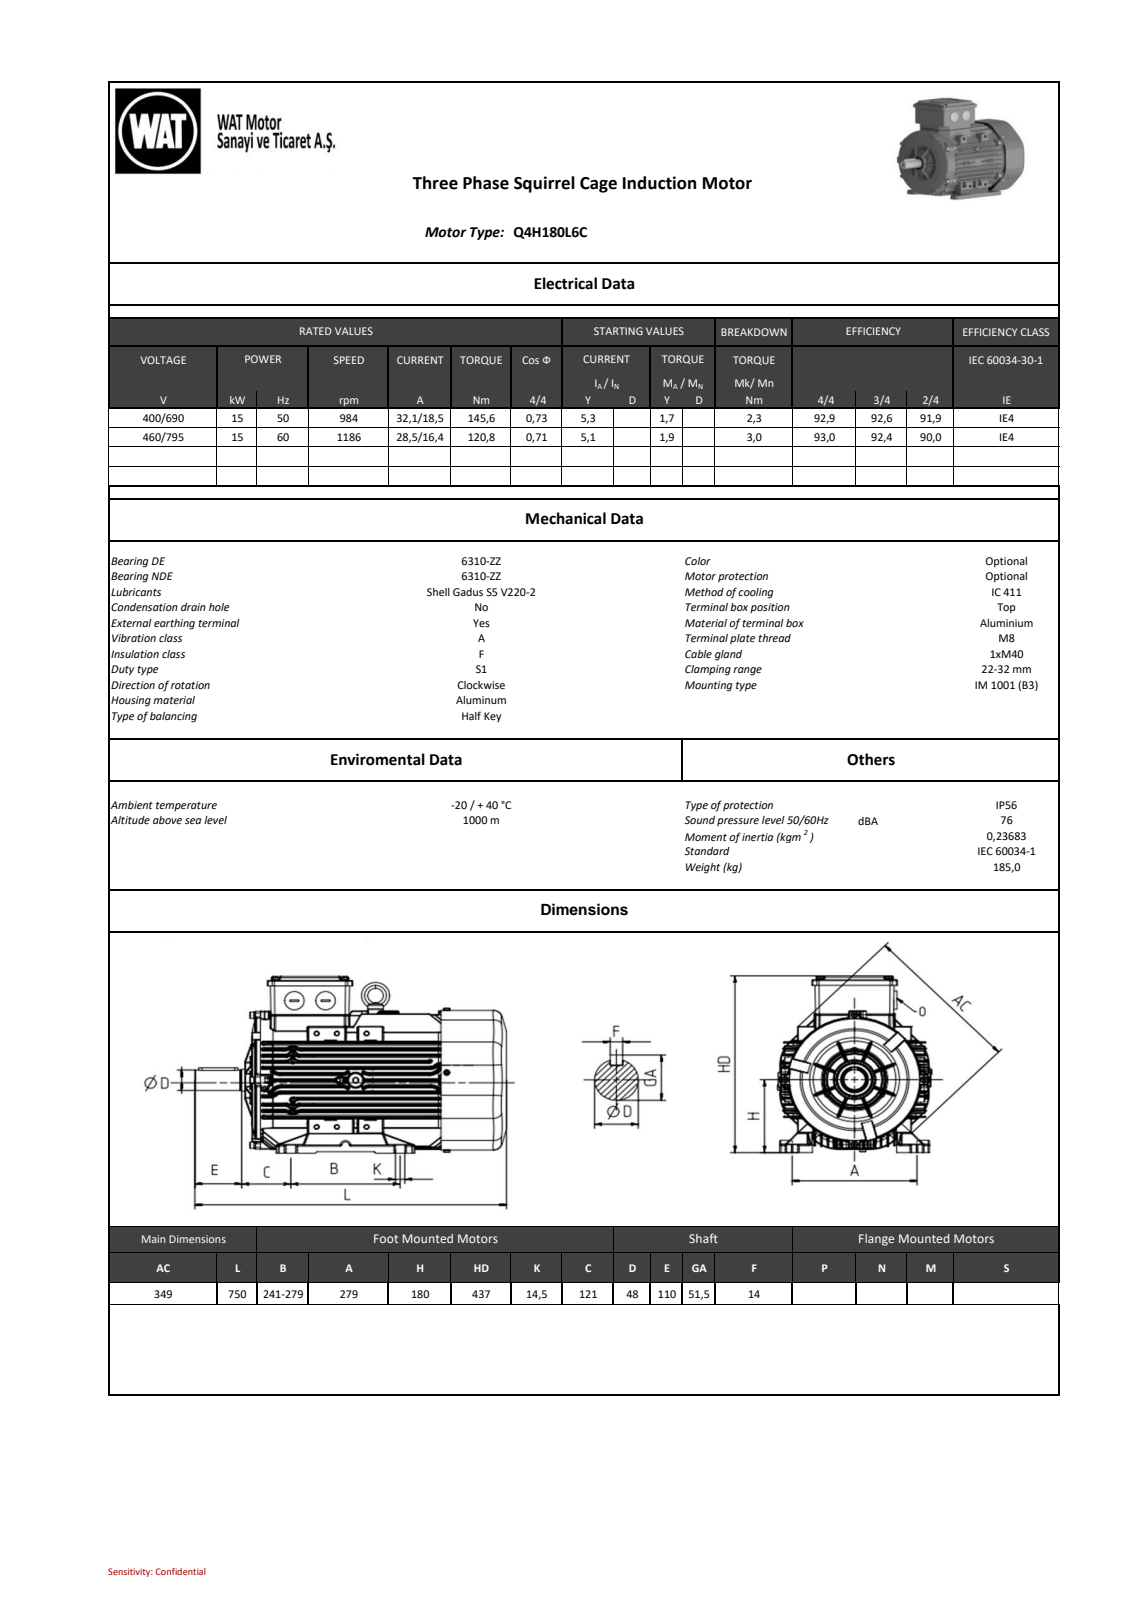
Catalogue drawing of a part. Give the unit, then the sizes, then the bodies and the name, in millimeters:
Units: millimetres
Overall size (bounding box): 749.5 × 433 × 347.31
Round holes (diameter × count): ⌀5.6 ×4, ⌀5.5 ×2, ⌀22 ×2, ⌀25.05 ×2, ⌀8 ×1, ⌀51 ×1, ⌀80 ×1, ⌀82 ×1, ⌀110 ×1, ⌀118 ×1
Round bosses / shafts (diameter × count): ⌀13 ×3, ⌀55 ×2, ⌀51.2 ×2, ⌀25 ×2, ⌀20 ×2, ⌀18.1 ×2, ⌀16 ×2, ⌀9.5 ×2
Partial cylindrical surfaces — rounded edges, fillets, slot ends (radius × count): R2 ×865, R1 ×817, R0.5 ×65, R5 ×58, R4 ×41, R8 ×22, R3 ×20, R1 ×18
Main face-to-face distances: 1.2, 16.21, 32.48, 16.27, 171.05, 173.83, 141.35, 157.62, 157.07, 140.86
Hole centre spacings: 1.94, 52, 91, 109.62, 109.64, 137.03, 156, 210.26
Bodies: 0 solids, 7665 faces (2558 planar, 2800 cylindrical, 2307 other)
Part name (STEP PRODUCT): 001_objects
STEP written by: SIEMENS PLM Software NX2206.8101 (AP203_CONFIGURATION_CONTROLLED_3D_DESIGN_OF_MECHANICAL_PARTS_AND_ASSEMBLIES_MIM_LF)
